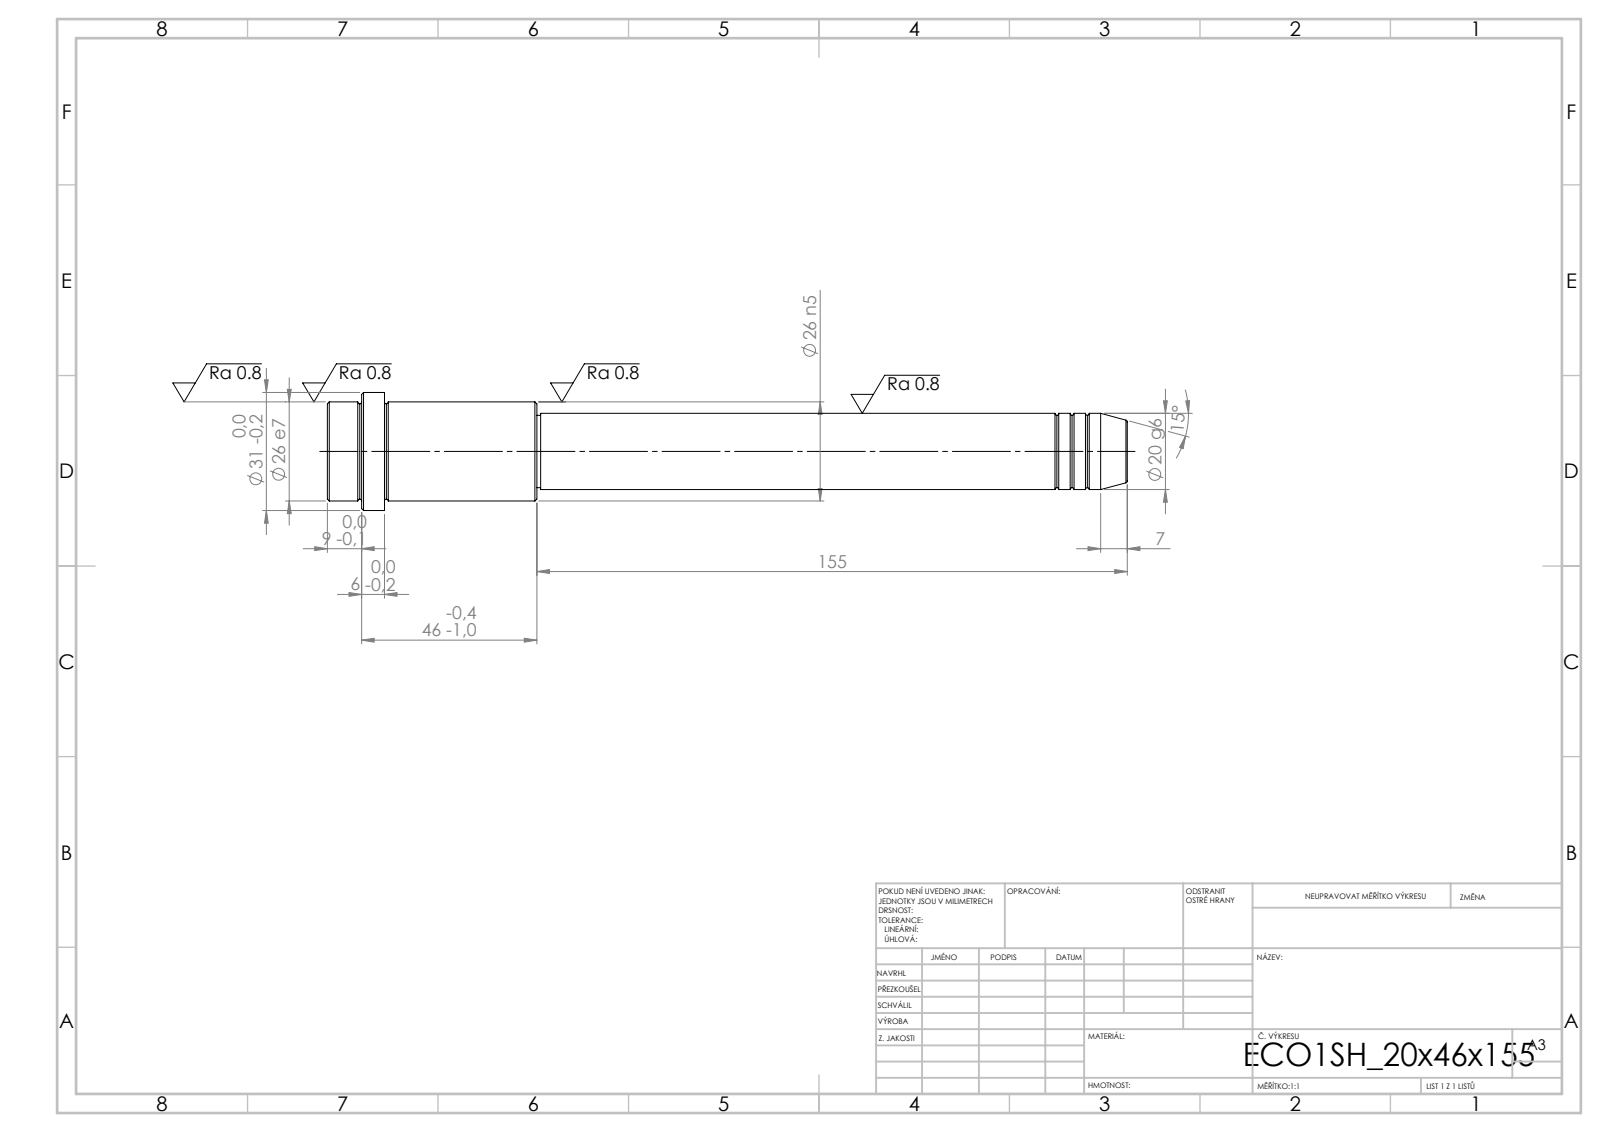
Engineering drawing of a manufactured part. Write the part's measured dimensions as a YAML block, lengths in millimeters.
step_written_by: "SolidWorks 2019 (CONFIG_CONTROL_DESIGN)"
units: millimeters
bodies: {solids: 1, faces: 52, planar: 6, cylindrical: 16, other: 30}
overall_size: [210, 31, 31]
volume: 78652
surface_area: 15861
round_bosses_or_shafts:
  - {diameter: 31, count: 1}
  - {diameter: 26, count: 1}
  - {diameter: 20, count: 1}
  - {diameter: 19, count: 1}
face_to_face_distances: [15, 40, 55, 155, 195, 210, 201, 46, 6, 9]
